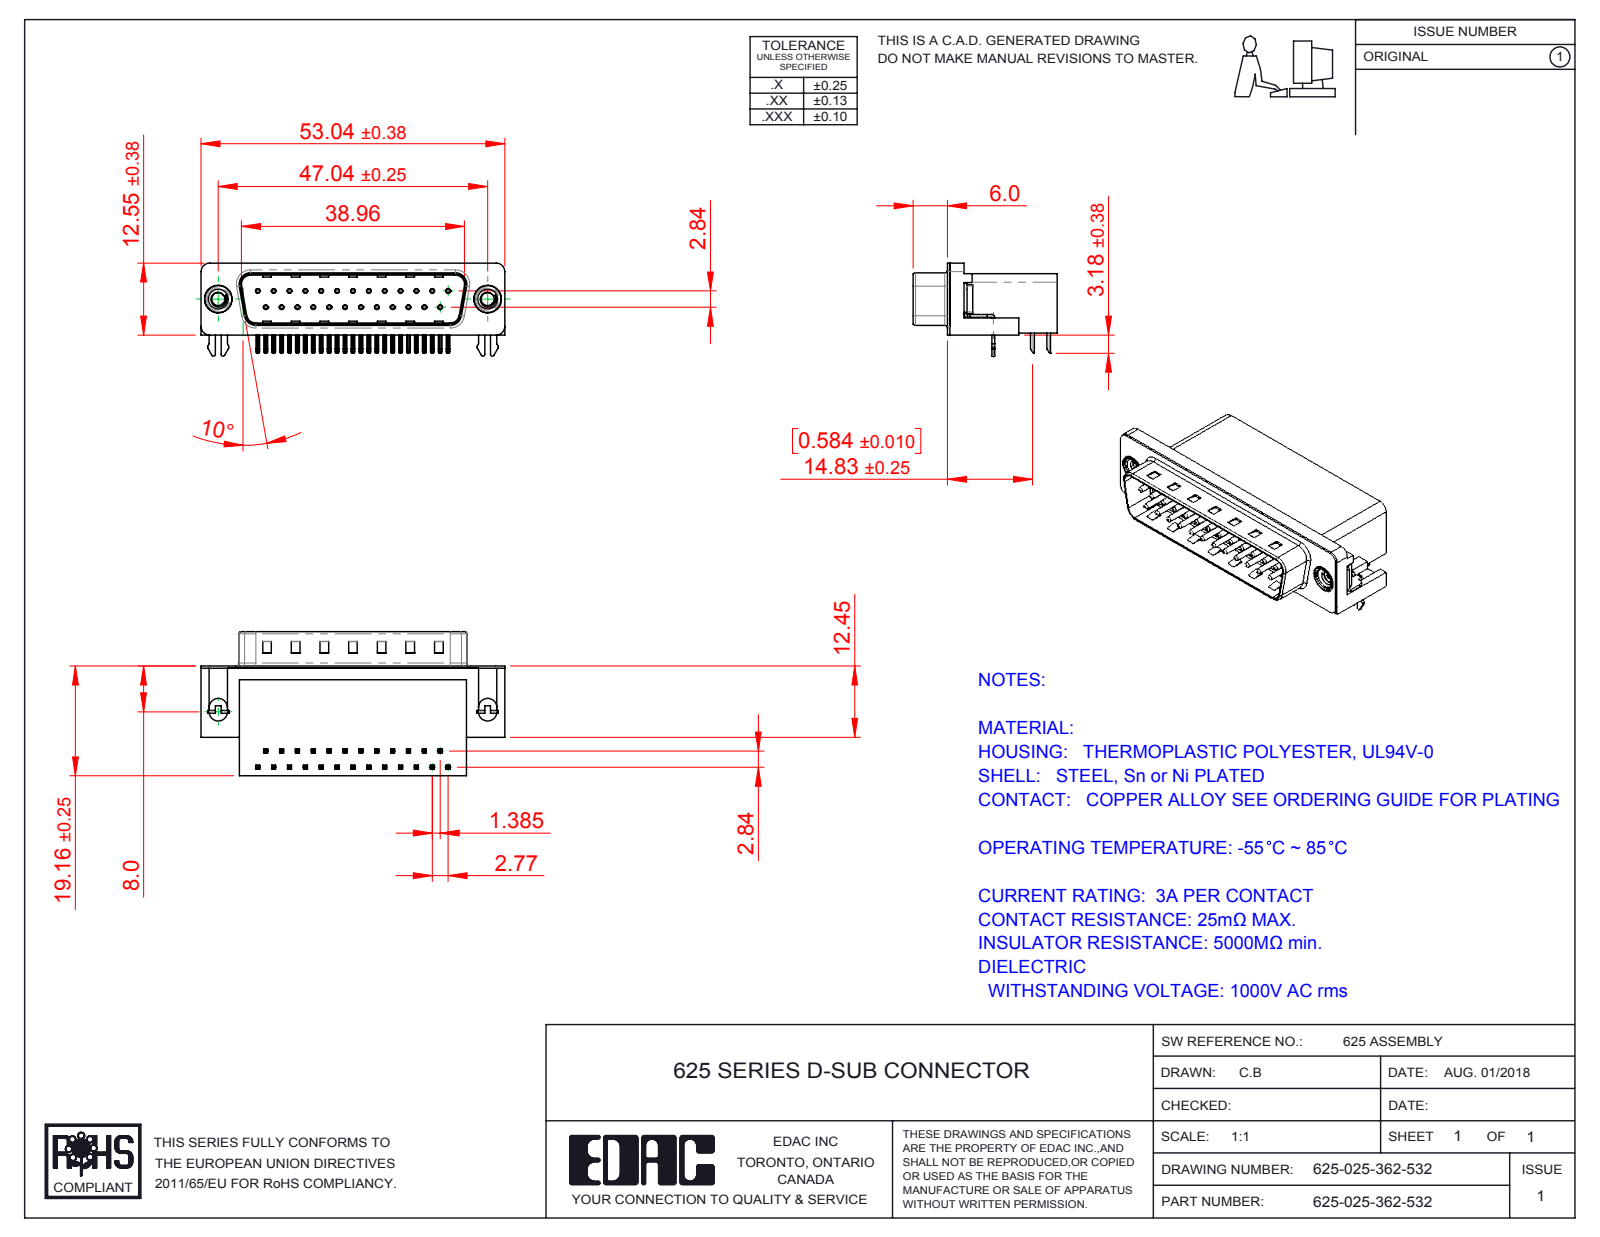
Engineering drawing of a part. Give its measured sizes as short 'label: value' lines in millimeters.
name: 625 4-40 Threaded Rivet; 625 Contact Top; 625 2 Prong Board Lock; 625 Housing_25 Socket (+3 more)
written by: SolidWorks 2016 (CONFIG_CONTROL_DESIGN)
unit: mm
bodies: 31 solids, 2305 faces (1437 planar, 669 cylindrical, 199 other)
size: 53.04 × 25.16 × 16.25
volume: 9 164 mm³; area: 8 868 mm²
holes: 25× ⌀0.35, 25× ⌀0.8, 2× ⌀2.26, 2× ⌀4, 2× ⌀4.8, 2× ⌀5
bosses: 25× ⌀0.75, 2× ⌀4.9, 2× ⌀4.75, 2× ⌀3.9
rounds: 108× R0.25, 50× R0.12, 16× R1, 14× R0.5, 8× R1.6, 7× R1.5, 4× R0.32, 4× R0.9
face distances: 0.4, 10.35, 18.76, 2.1, 8.76, 10.46, 10.86, 1.7, 19.16, 10.11
hole spacings: 3.16, 2.77, 11.08, 5.54, 8.31, 5.03, 13.85, 7.48
